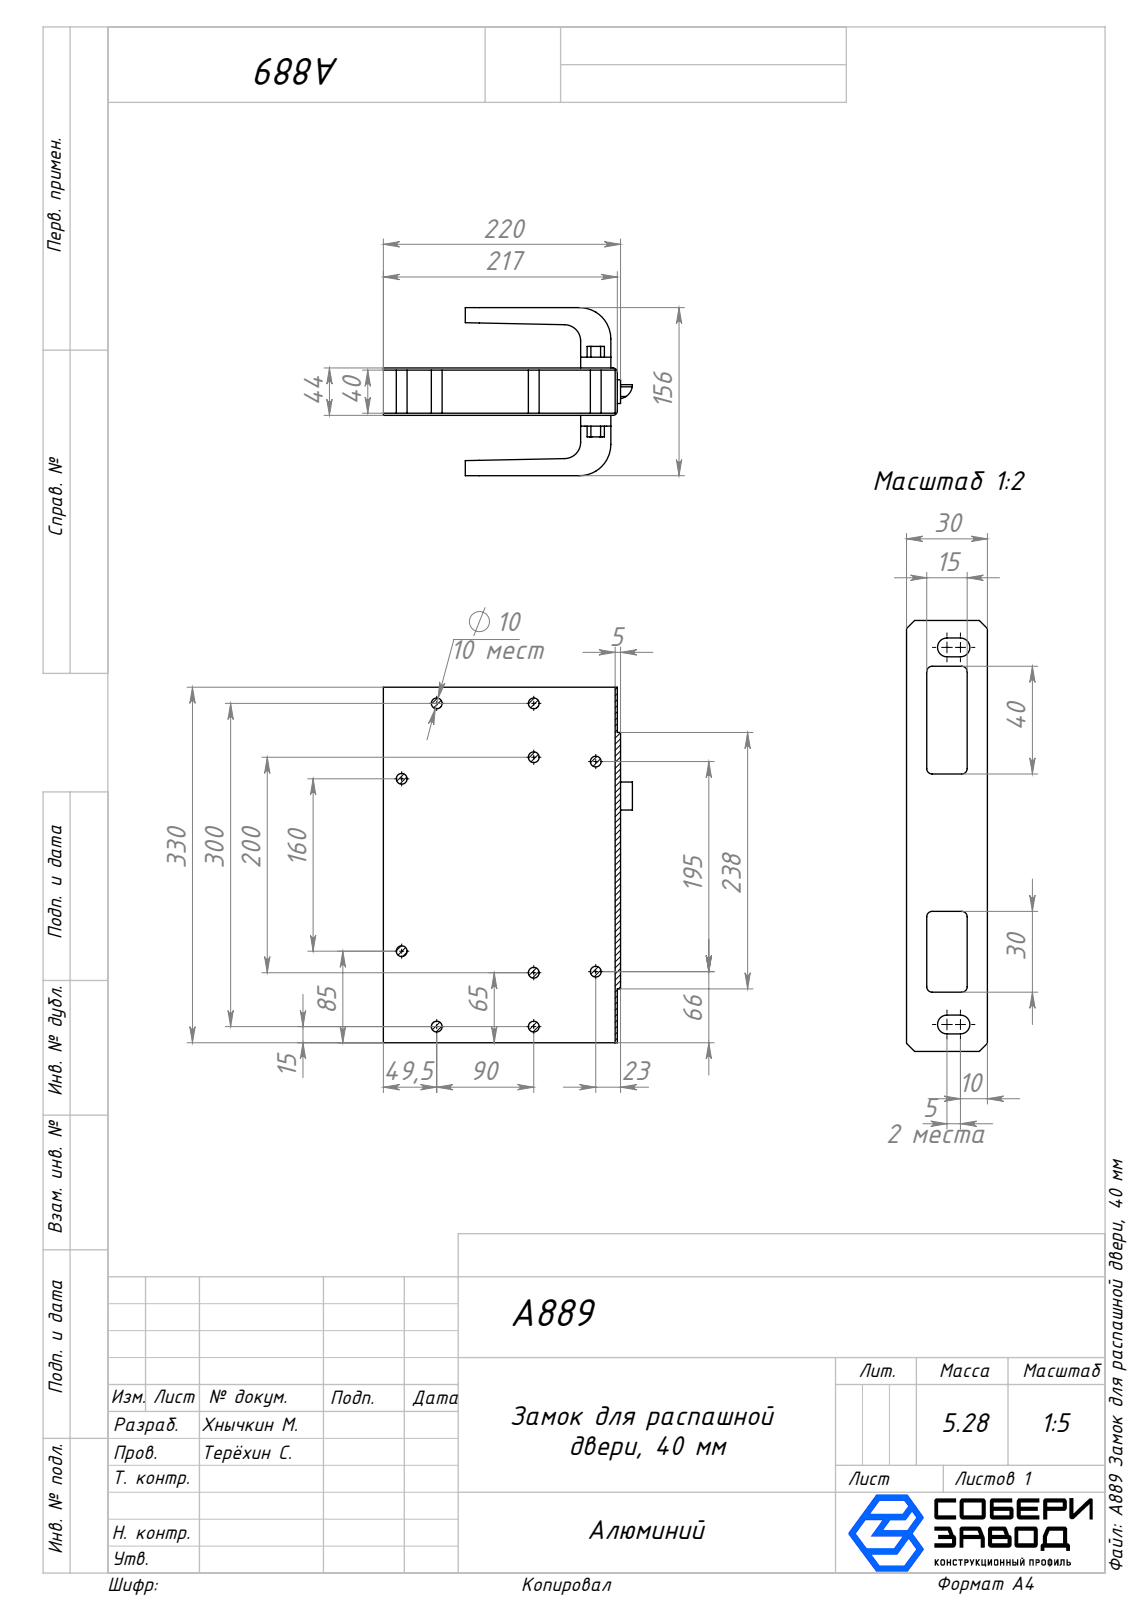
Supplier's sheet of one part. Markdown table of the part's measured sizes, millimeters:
| quantity | value |
| --- | --- |
| part name | A889 Замок для распашной двери, 40 мм |
| STEP written by | SolidWorks 2025 (AUTOMOTIVE_DESIGN) |
| units | millimeters |
| bodies | 1 solid, 101 faces (48 planar, 53 cylindrical, 0 other) |
| overall size | 330 × 231 × 156 |
| volume | 635 296 mm³ |
| surface area | 364 971 mm² |
| round bosses / shafts (diameter × count) | 10 × 10 |
| partial cylindrical surfaces (radius × count) | 4 × 6, 1 × 2, 4.64 × 2, 5.49 × 2, 15.07 × 2, 29 × 2, 8 × 1, 13 × 1 |
| main face-to-face distances | 2, 42, 40, 44, 10, 12, 52, 54, 9, 64 |
